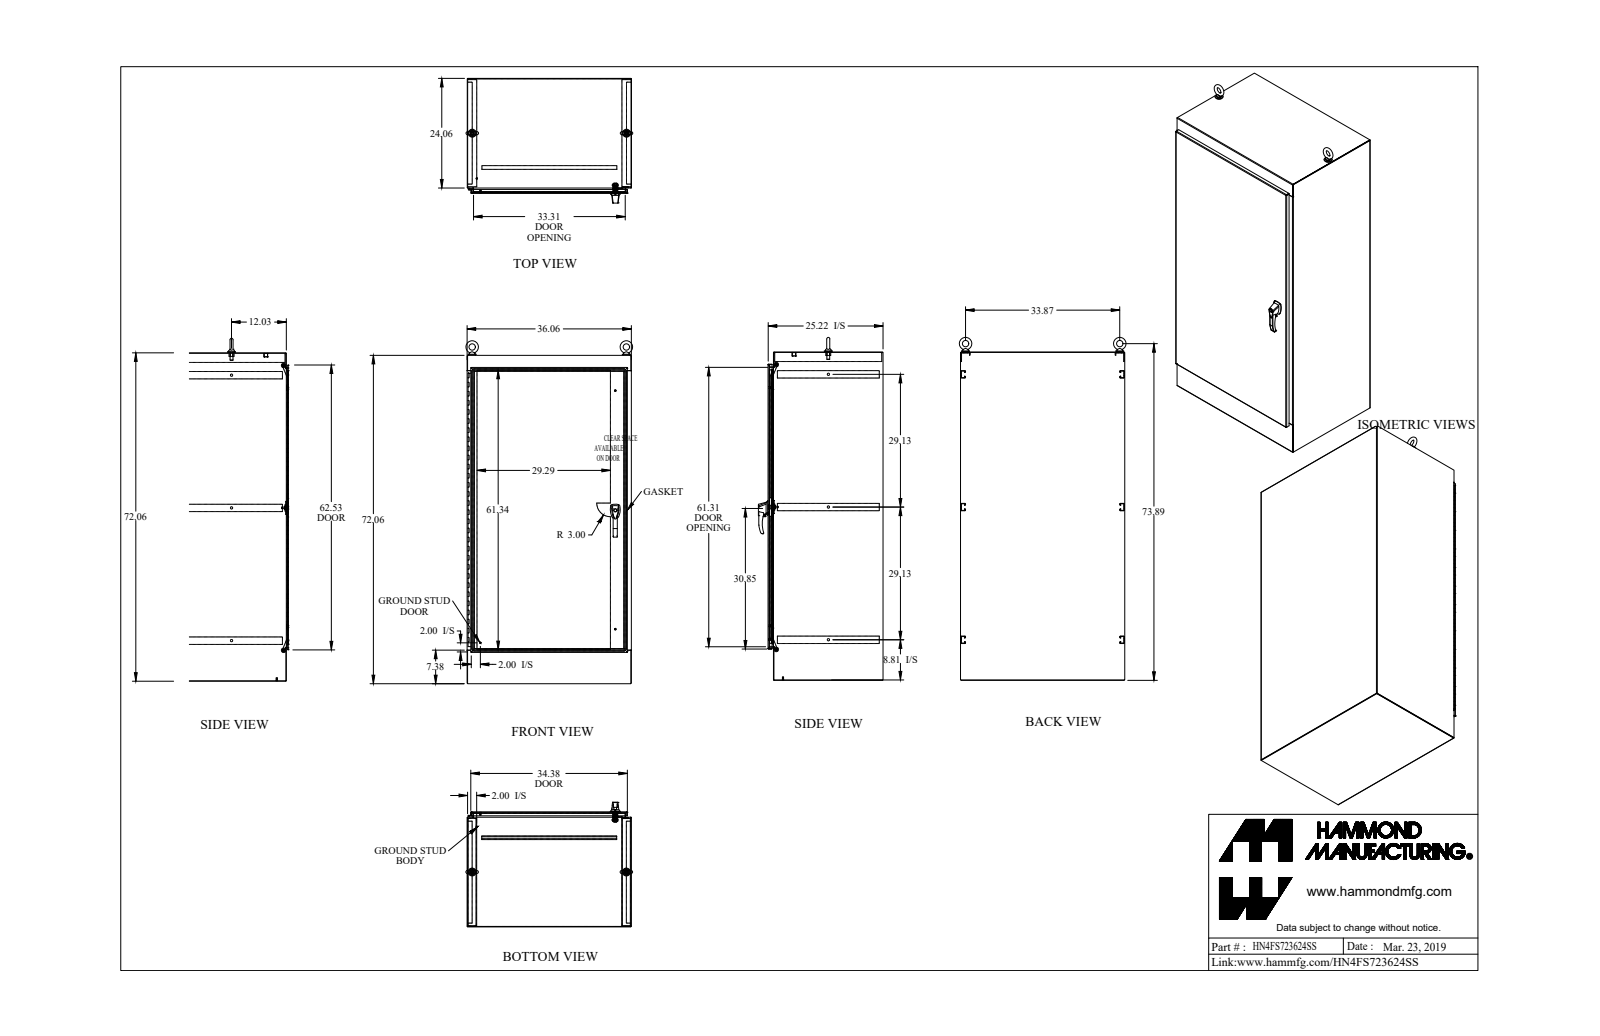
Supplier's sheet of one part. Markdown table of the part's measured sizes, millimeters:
| quantity | value |
| --- | --- |
| part name | HN4FS723624SS |
| STEP written by | SolidWorks 2018 (AUTOMOTIVE_DESIGN) |
| units | millimeters |
| bodies | 53 solids, 1874 faces (869 planar, 840 cylindrical, 165 other) |
| overall size | 1917.4 × 929.7 × 695 |
| volume | 19 350 000 mm³ |
| surface area | 16 000 000 mm² |
| round holes (diameter × count) | 7.7 × 10, 8.9 × 7, 12.7 × 3, 6.4 × 2, 6.5 × 2, 7.1 × 2, 7.1 × 2, 8 × 2, 9.9 × 2, 10.5 × 2, 13.4 × 2, 15.9 × 2 |
| round bosses / shafts (diameter × count) | 44.5 × 2, 38.1 × 2, 31.8 × 2, 25.4 × 2, 19.1 × 2, 18.7 × 2, 16 × 2, 15.9 × 2 |
| partial cylindrical surfaces (radius × count) | 1.1 × 42, 3.5 × 36, 12.7 × 23, 3.2 × 22, 0.5 × 16, 1.2 × 15, 1.5 × 15, 3.6 × 15 |
| main face-to-face distances | 2.4, 638.9, 913.5, 636.4, 641.3, 911.1, 1827.9, 915.9, 608.7, 30.1 |
| hole center spacings | 152.4, 304.8, 457.2, 609.6, 762, 914.4, 1066.8, 0.4 |
